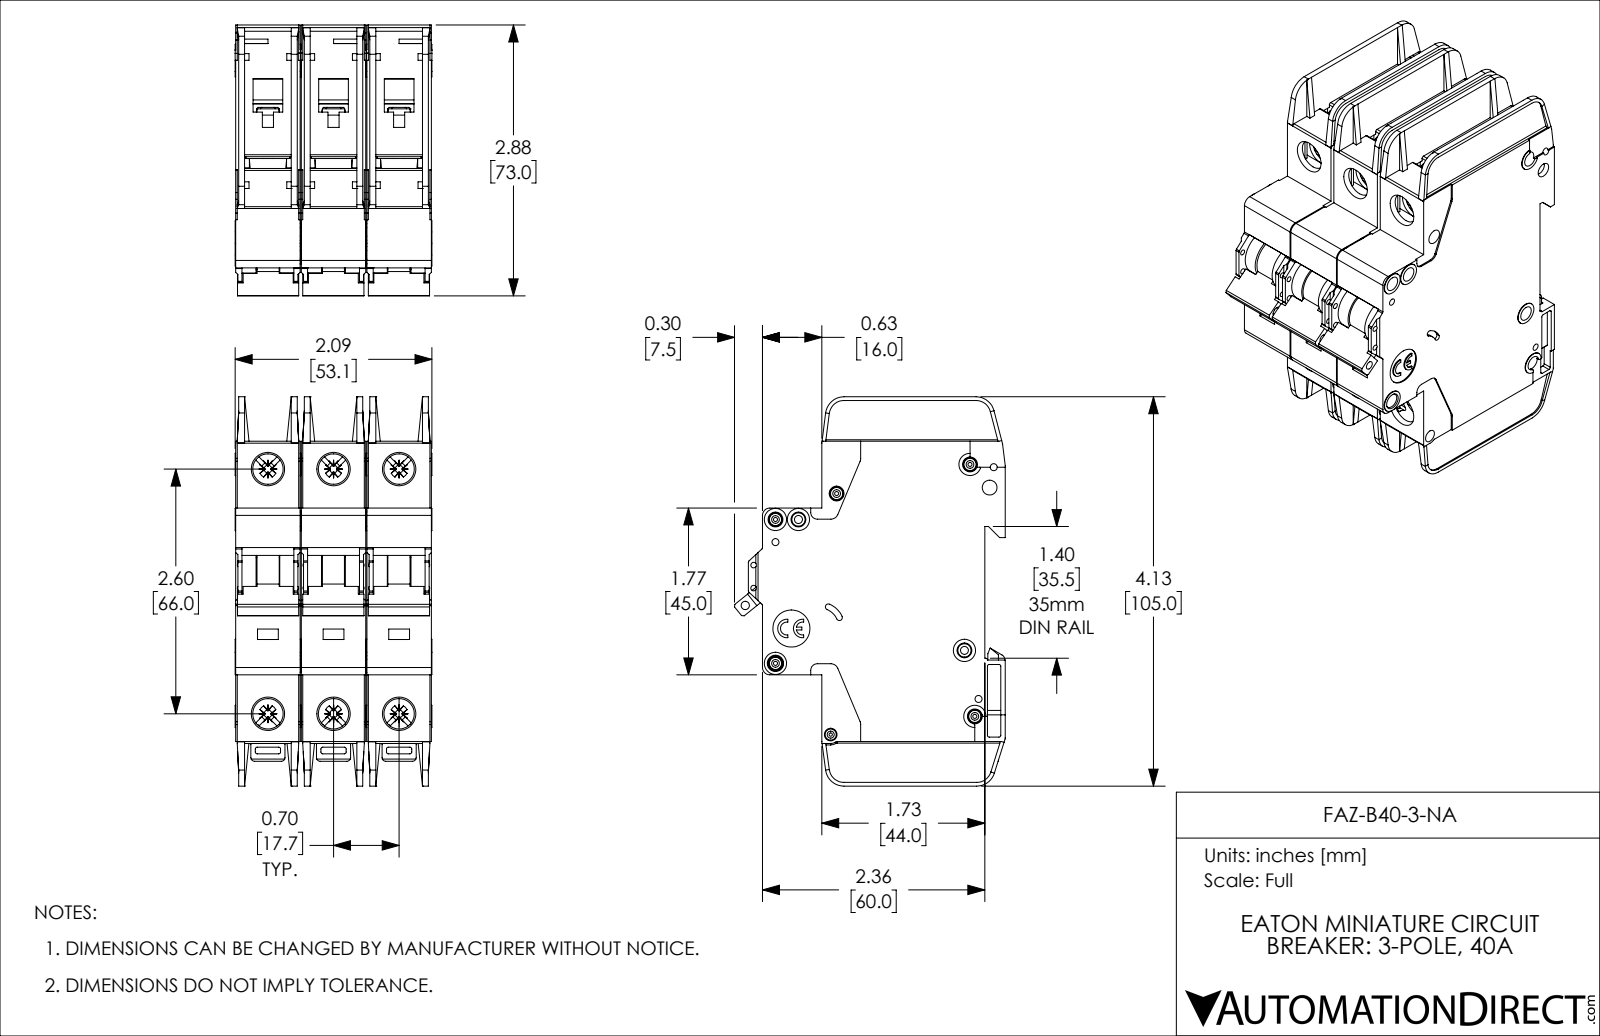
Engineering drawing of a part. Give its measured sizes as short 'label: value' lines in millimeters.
name: FAZ-B40-3-NA
written by: SolidWorks 2019 (AUTOMOTIVE_DESIGN)
unit: mm
bodies: 3 solids, 3381 faces (2013 planar, 1071 cylindrical, 297 other)
size: 105 × 73.1 × 53.1
volume: 230 200 mm³; area: 79 350 mm²
holes: 8× ⌀4, 6× ⌀8.2, 5× ⌀1.1, 4× ⌀1.9, 2× ⌀1.5, 2× ⌀2.2, 1× ⌀0.9, 1× ⌀2.3, 1× ⌀2.5, 1× ⌀3.4, 1× ⌀10
bosses: 5× ⌀3.3, 4× ⌀6, 4× ⌀3, 3× ⌀2.5
rounds: 72× R0.5, 30× R0.4, 18× R1, 12× R1.1, 12× R2, 6× R0.2, 6× R0.3, 6× R0.7
face distances: 17.7, 1.2, 35.4, 17.4, 15, 35.1, 18.9, 16.5, 2.7, 2.4
hole spacings: 17.7, 68.3, 66, 6.2, 13.6, 22.1, 35.4, 74.9
